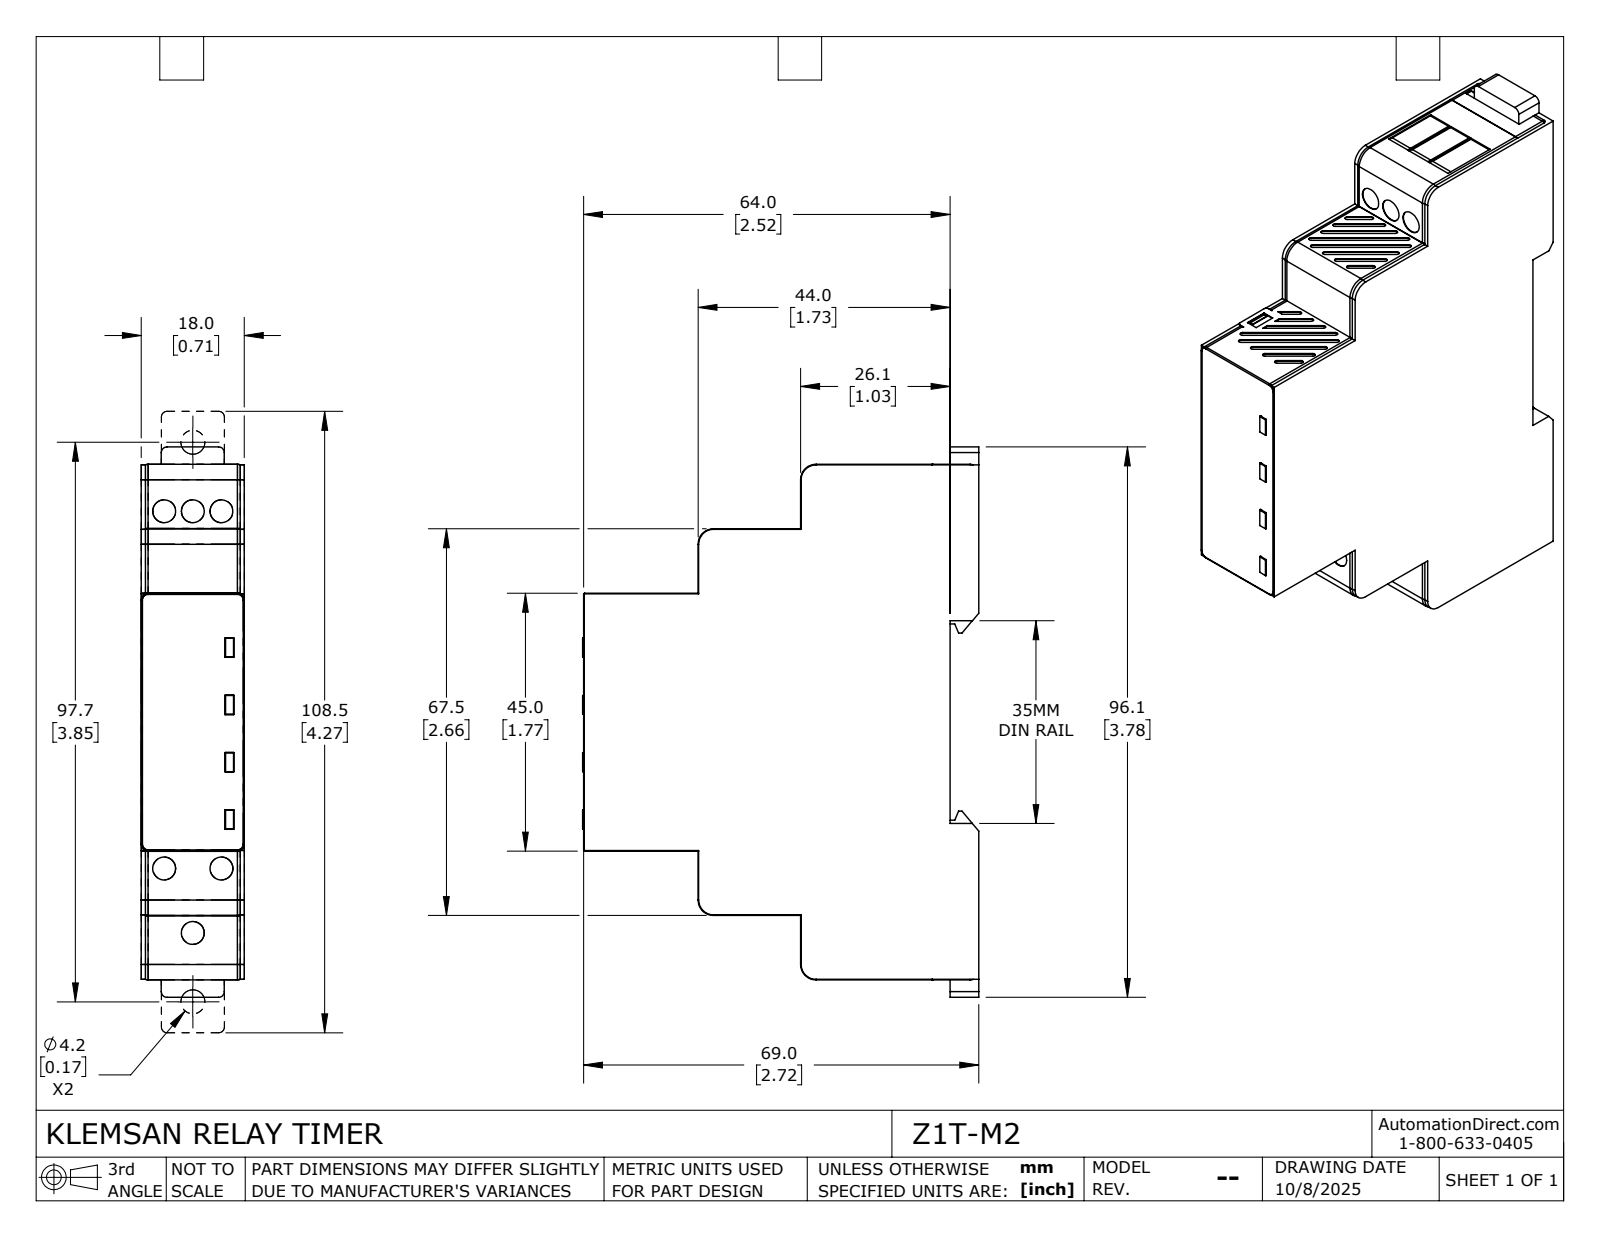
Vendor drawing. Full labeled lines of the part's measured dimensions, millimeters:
Part name (STEP PRODUCT): Z1T-M2
STEP written by: SolidWorks 2024 (CONFIG_CONTROL_DESIGN)
Units: millimetres
Bodies: 3 solids, 440 faces (280 planar, 60 cylindrical, 100 other)
Overall size (bounding box): 96.07 × 69.15 × 18
Volume: 83 847 mm³ · Surface area: 17 884 mm²
Round holes (diameter × count): ⌀4.2 ×2, ⌀4 ×1
Partial cylindrical surfaces — rounded edges, fillets, slot ends (radius × count): R1.2 ×16, R0.2 ×4, R1 ×4, R2.6 ×4, R2.7 ×4, R0.5 ×2, R1.5 ×2
Main face-to-face distances: 18, 3.5, 14.5, 11.25, 64, 5, 69, 22.5, 67.4, 67.5
Hole centre spacings: 5.83, 79.43, 85.26
